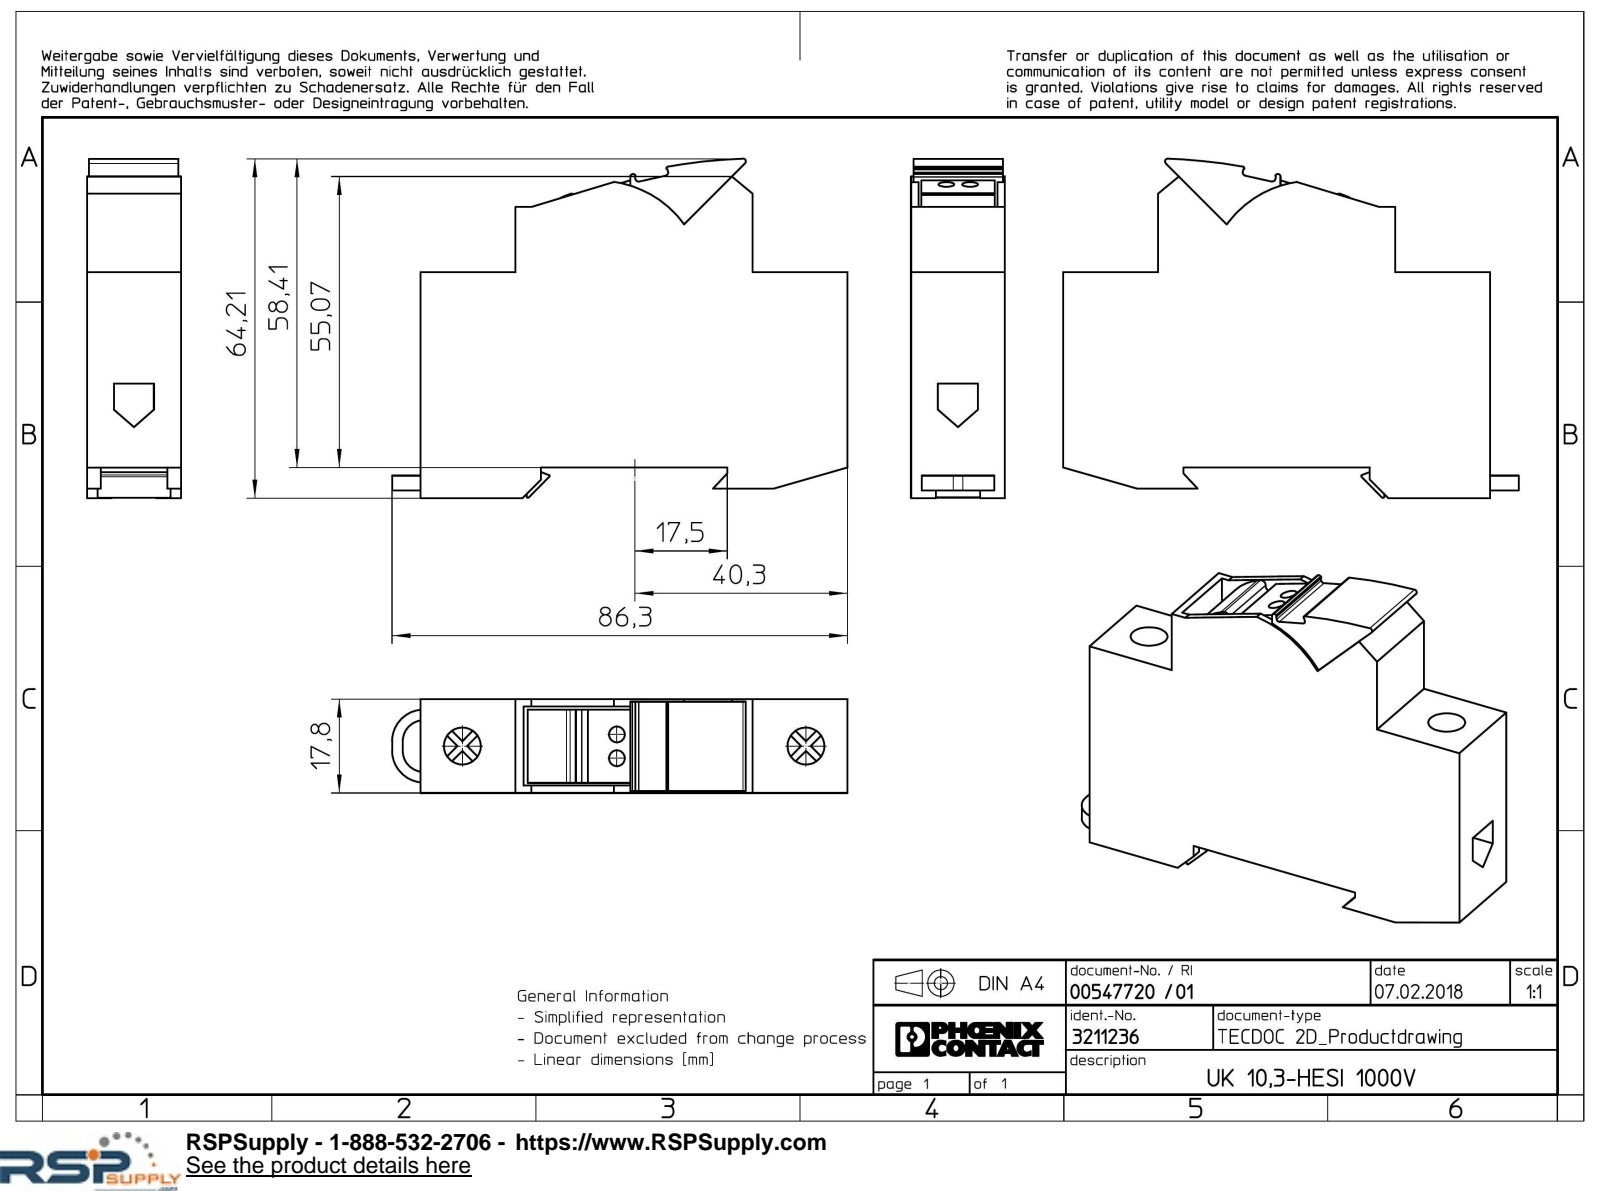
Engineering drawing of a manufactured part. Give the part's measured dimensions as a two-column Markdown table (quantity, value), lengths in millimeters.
| quantity | value |
| --- | --- |
| part name | UK_10.3-HESI_1000V-select |
| STEP written by | Creo Elements/Direct Modeling 18.1I 14-Aug-2016 (C) Parametric Technology GmbH (AUTOMOTIVE_DESIGN) |
| units | millimeters |
| bodies | 1 solid, 132 faces (101 planar, 31 cylindrical, 0 other) |
| overall size | 86.3 × 64.21 × 17.8 |
| volume | 66 408 mm³ |
| surface area | 15 667 mm² |
| round holes (diameter × count) | 3 × 2, 7 × 2 |
| partial cylindrical surfaces (radius × count) | 0.5 × 4, 0.15 × 2, 0.2 × 2, 0.4 × 2, 1.1 × 2, 4 × 2, 6 × 2, 0.8 × 1 |
| main face-to-face distances | 17.8, 80.9, 15.9, 37, 18, 62.9, 12.7, 5.1, 1.4, 16.4 |
| hole center spacings | 35.92, 4.5, 29.33, 29.34, 65.1 |
